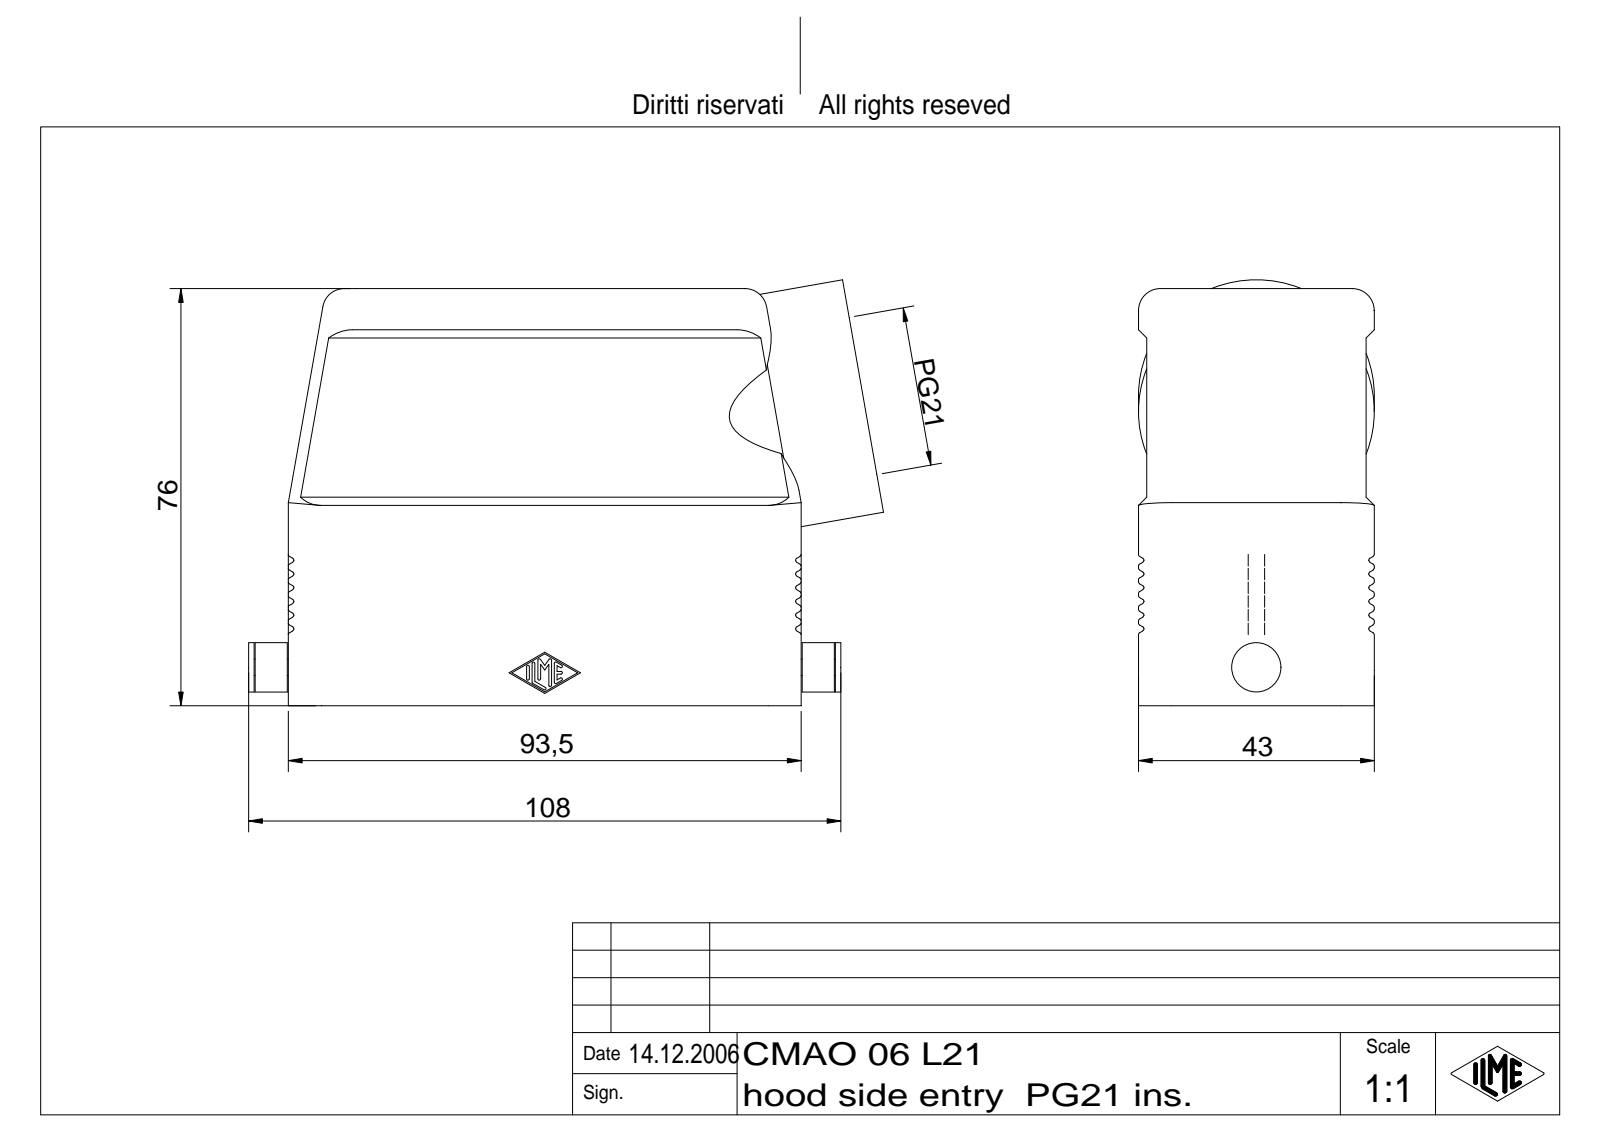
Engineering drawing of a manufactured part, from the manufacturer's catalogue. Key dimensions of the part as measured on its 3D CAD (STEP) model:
Part name (STEP PRODUCT): CMAO 06 L21
STEP written by: Autodesk Inventor 7 (AUTOMOTIVE_DESIGN)
Units: millimetres
Bodies: 1 solid, 857 faces (154 planar, 424 cylindrical, 279 other)
Overall size (bounding box): 115.77 × 77.61 × 43
Volume: 82 277 mm³ · Surface area: 49 357 mm²
Round holes (diameter × count): ⌀25 ×1, ⌀26.78 ×1
Round bosses / shafts (diameter × count): ⌀43 ×1, ⌀9 ×1, ⌀3 ×1
Partial cylindrical surfaces — rounded edges, fillets, slot ends (radius × count): R0.4 ×96, R0.25 ×14, R6 ×8, R1.5 ×4, R3 ×4, R4 ×4, R5 ×2
Main face-to-face distances: 1.5, 3, 40, 37, 38.5, 41.5, 43, 90.5, 79.25, 82.25
